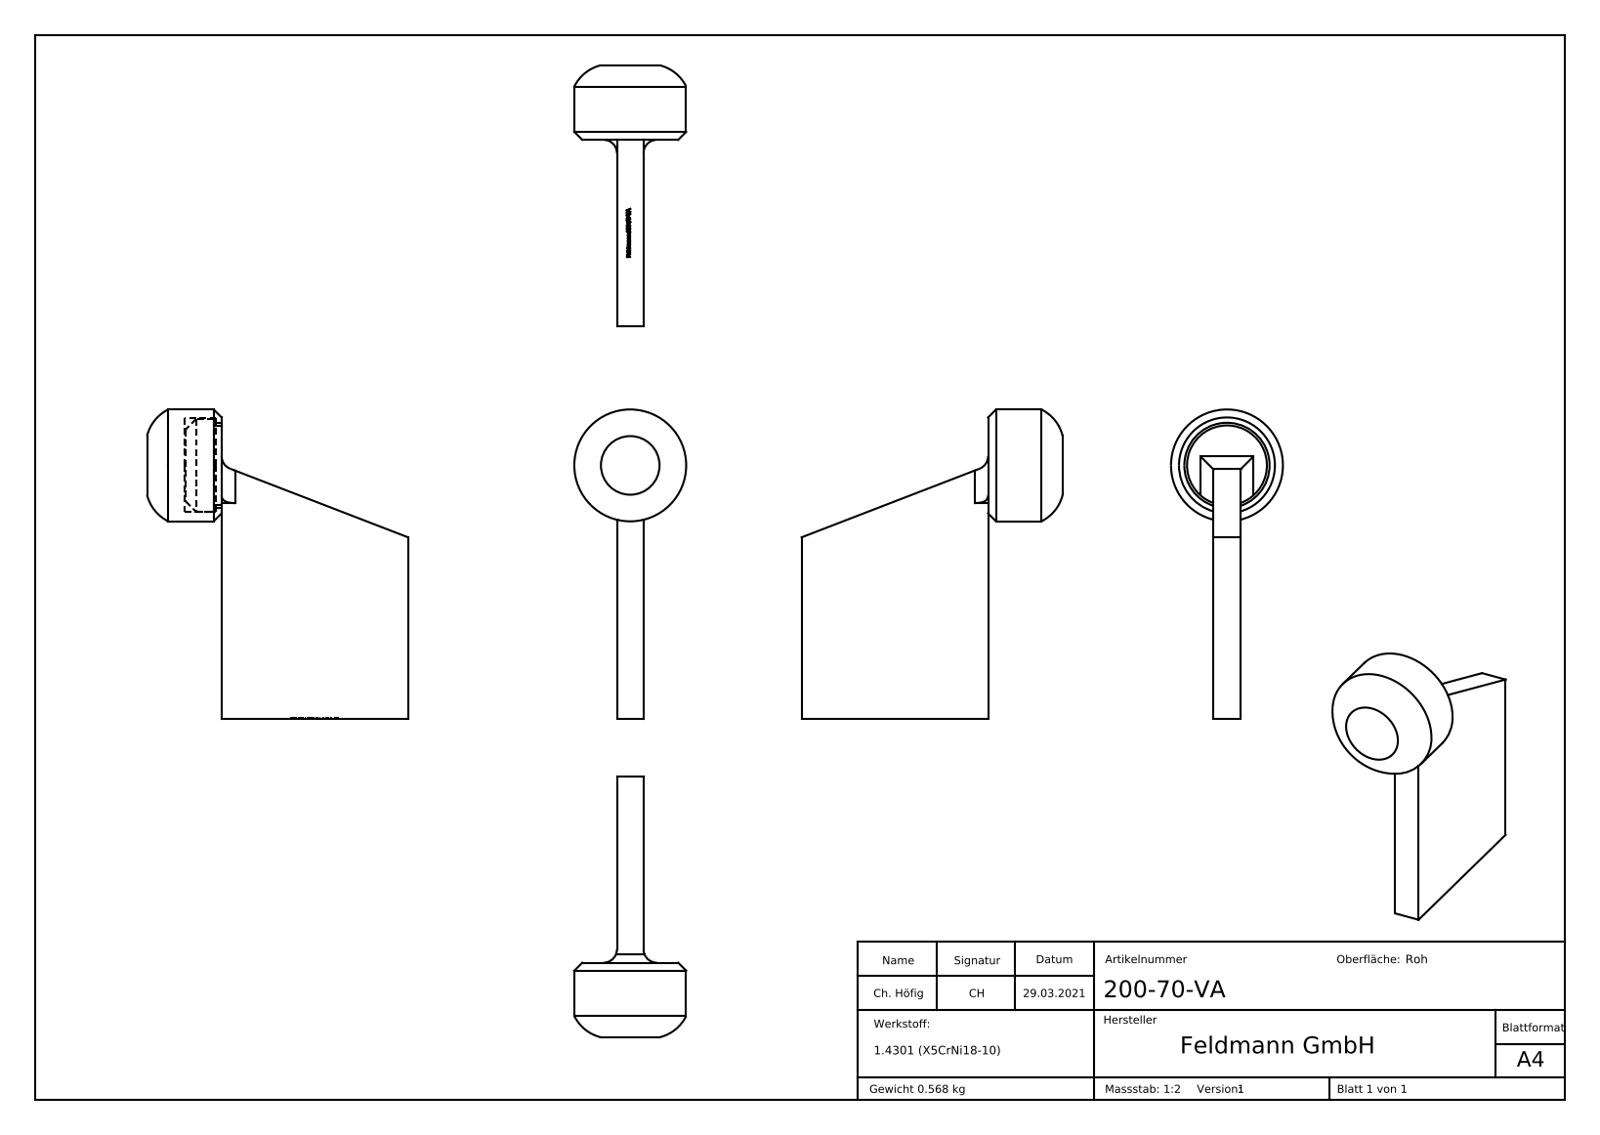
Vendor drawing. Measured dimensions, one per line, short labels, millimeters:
name: 200-70-VA Teil 1_200-70-VA Teil1; 200-70-VA Teil 1; 200-70-VA; 200-70-VA Teil 2_200-70-VA Teil 2 (+1 more)
written by: SolidWorks 2018 (CONFIG_CONTROL_DESIGN)
unit: mm
bodies: 2 solids, 229 faces (129 planar, 13 cylindrical, 87 other)
size: 116 × 98 × 42
volume: 90 458 mm³; area: 24 646 mm²
holes: 1× ⌀32, 1× ⌀35.2
bosses: 1× ⌀42, 1× ⌀35, 1× ⌀30
rounds: 3× R5
face distances: 10, 14, 70, 84, 0.5, 83.5, 13.5, 28, 98, 14.5
